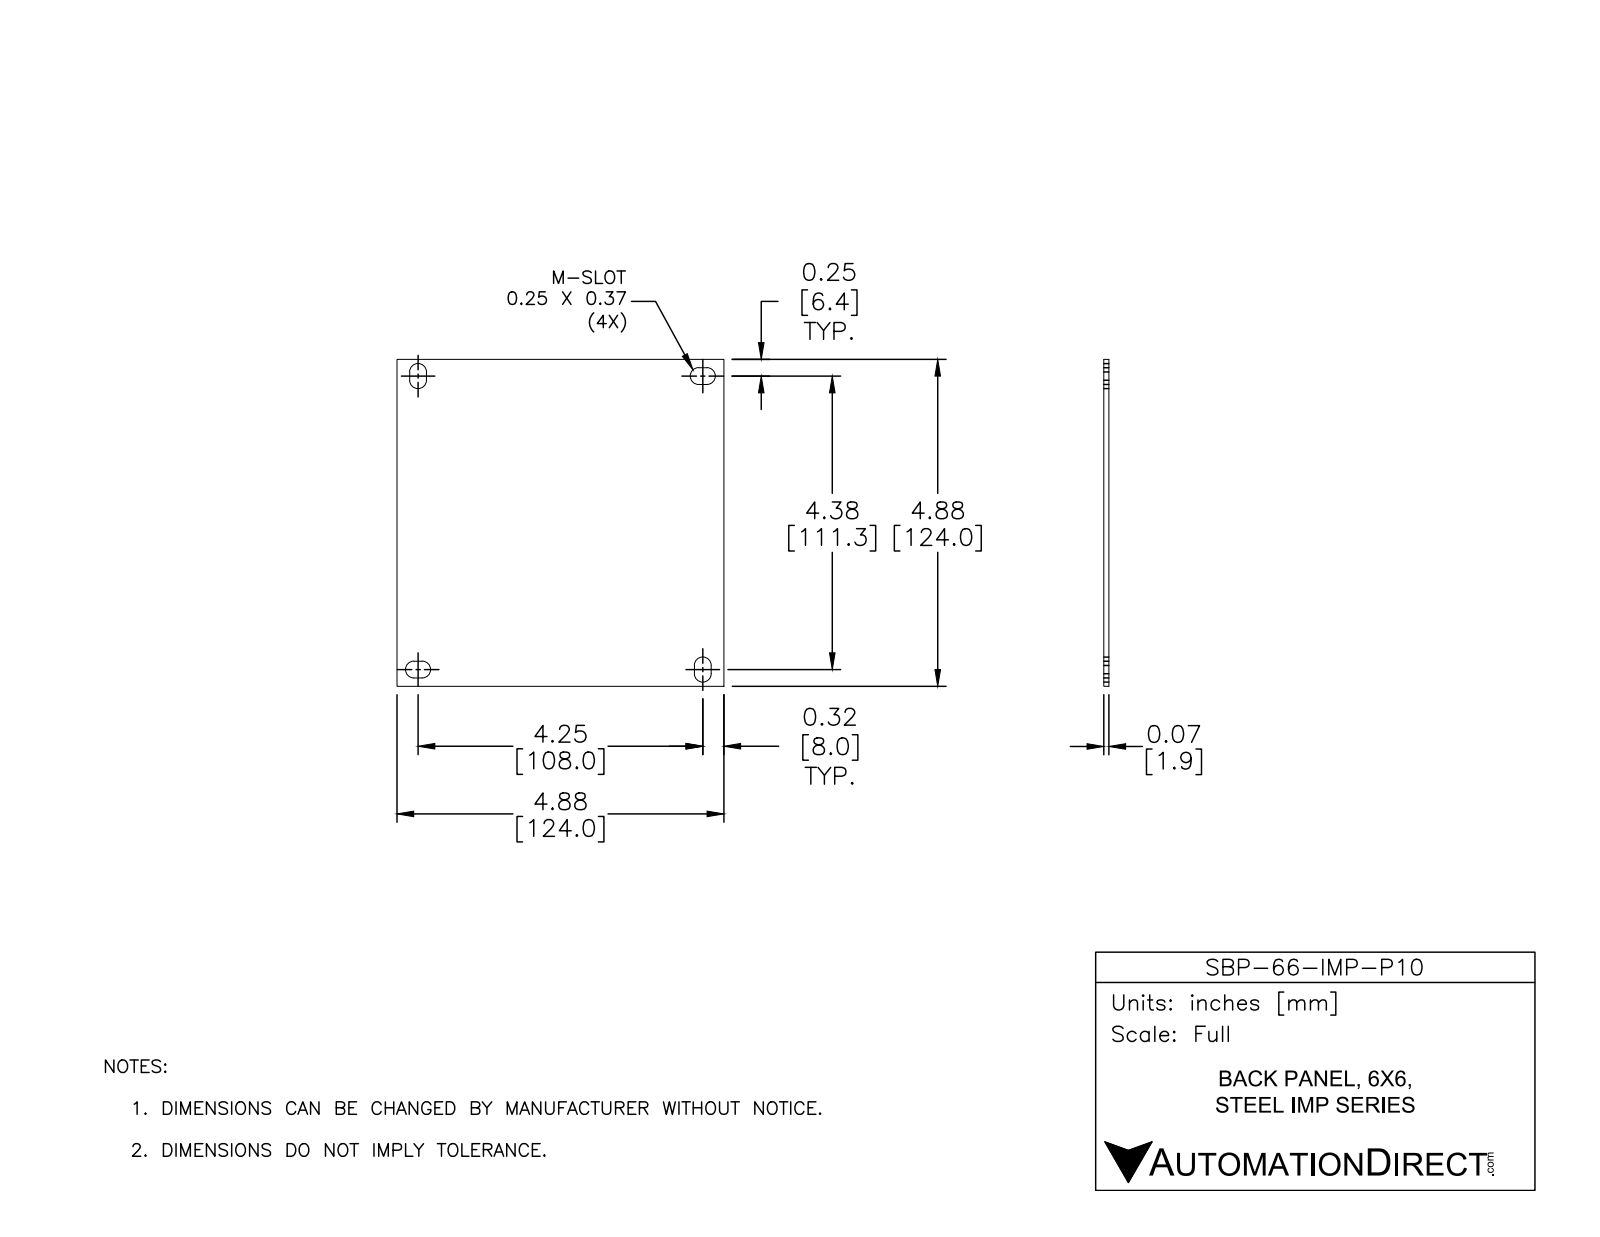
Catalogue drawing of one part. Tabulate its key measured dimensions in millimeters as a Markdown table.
| quantity | value |
| --- | --- |
| part name | SBP-66-IMP-P604 |
| STEP written by | SolidWorks 2016 (AUTOMOTIVE_DESIGN) |
| units | millimeters |
| bodies | 1 solid, 24 faces (14 planar, 10 cylindrical, 0 other) |
| overall size | 124 × 124 × 1.6 |
| volume | 24 680 mm³ |
| surface area | 31 300 mm² |
| partial cylindrical surfaces (radius × count) | 3.2 × 8 |
| main face-to-face distances | 1.6, 124, 6.4, 3.2, 9.5, 114.4, 120.8, 111.3, 108, 117.6 |
